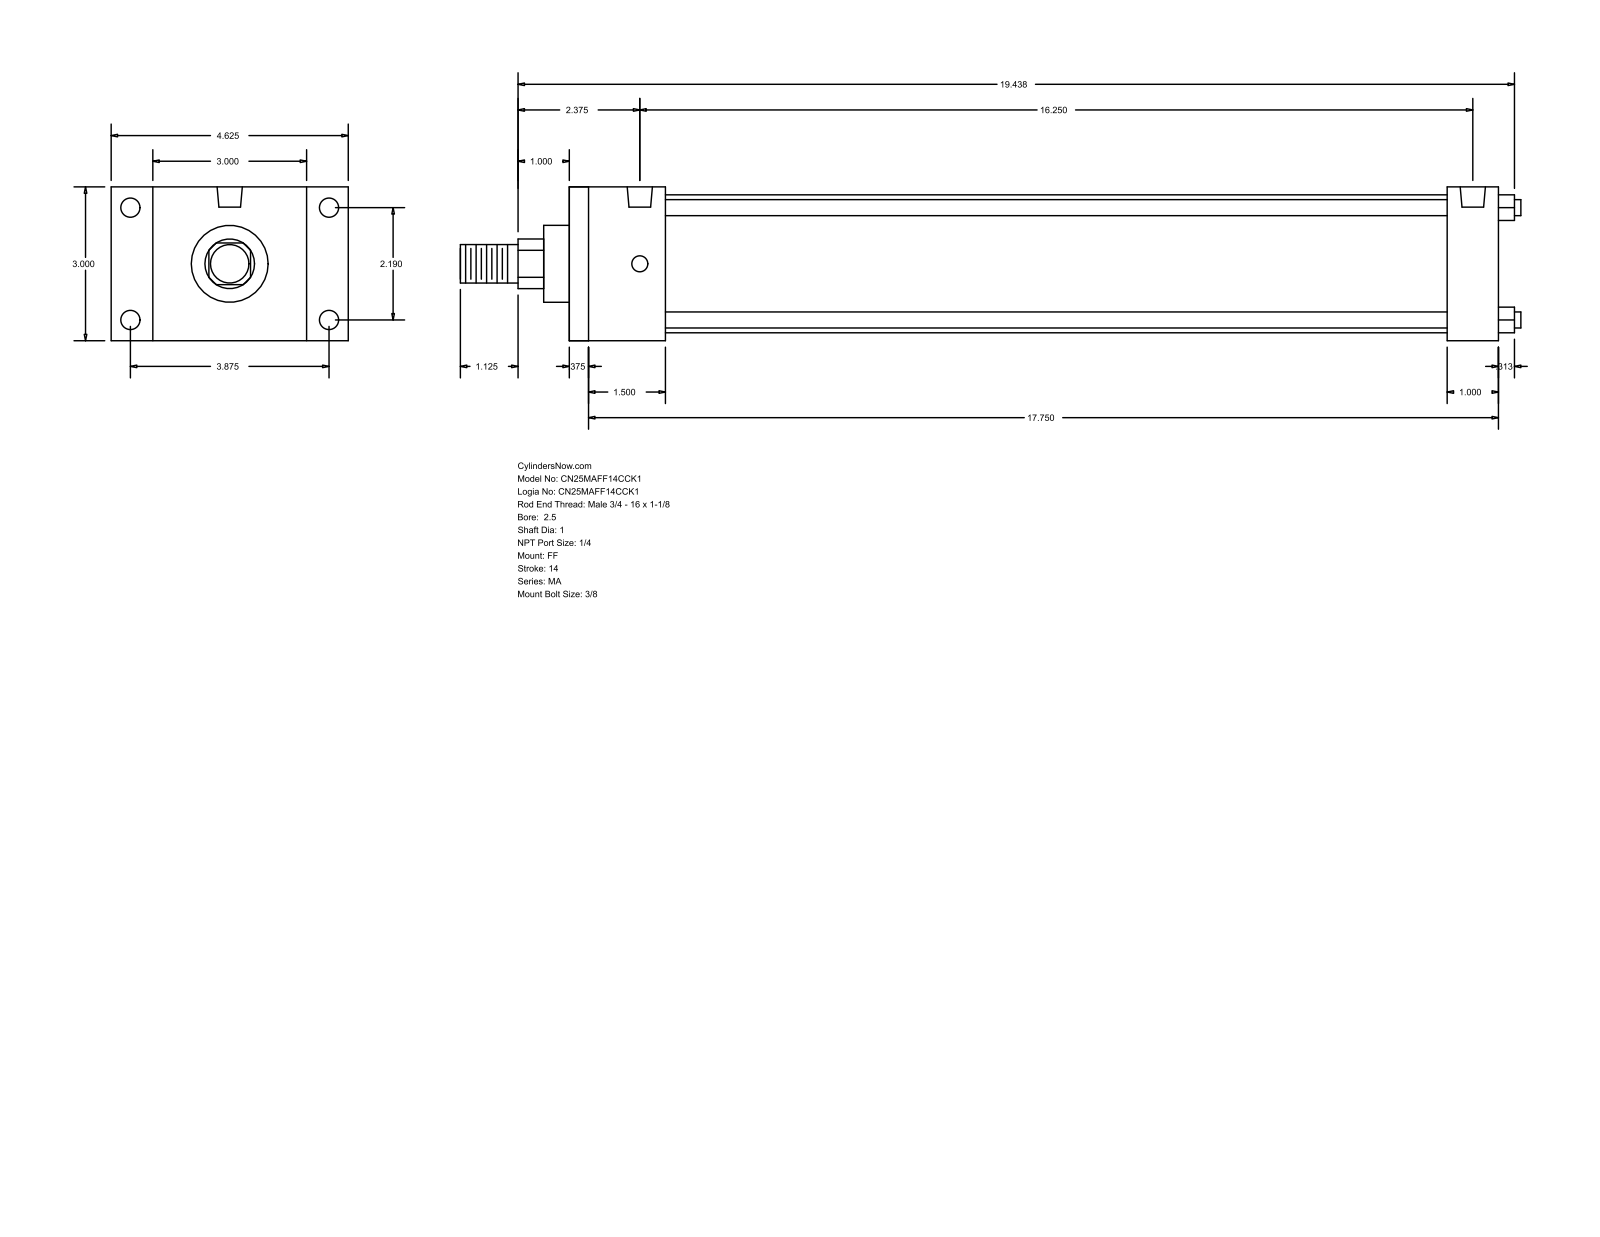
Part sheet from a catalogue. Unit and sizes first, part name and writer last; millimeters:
Units: millimetres
Overall size (bounding box): 525.46 × 117.47 × 76.2
Round holes (diameter × count): ⌀7.94 ×4, ⌀9.53 ×4, ⌀12.49 ×2
Round bosses / shafts (diameter × count): ⌀7.94 ×4, ⌀68.33 ×1, ⌀38.1 ×1, ⌀25.4 ×1, ⌀19.05 ×1
Partial cylindrical surfaces — rounded edges, fillets, slot ends (radius × count): R12.29 ×1
Main face-to-face distances: 76.2, 460.37, 450.85, 9.52, 25.39, 47.63, 434.98, 38.11, 425.46, 387.35
Hole centre spacings: 55.62, 98.42, 113.05, 412.74
Bodies: 0 solids, 92 faces (64 planar, 28 cylindrical, 0 other)
Part name (STEP PRODUCT): MA_FF__0250_1
STEP written by: GSSL Pune (CONFIG_CONTROL_DESIGN)
